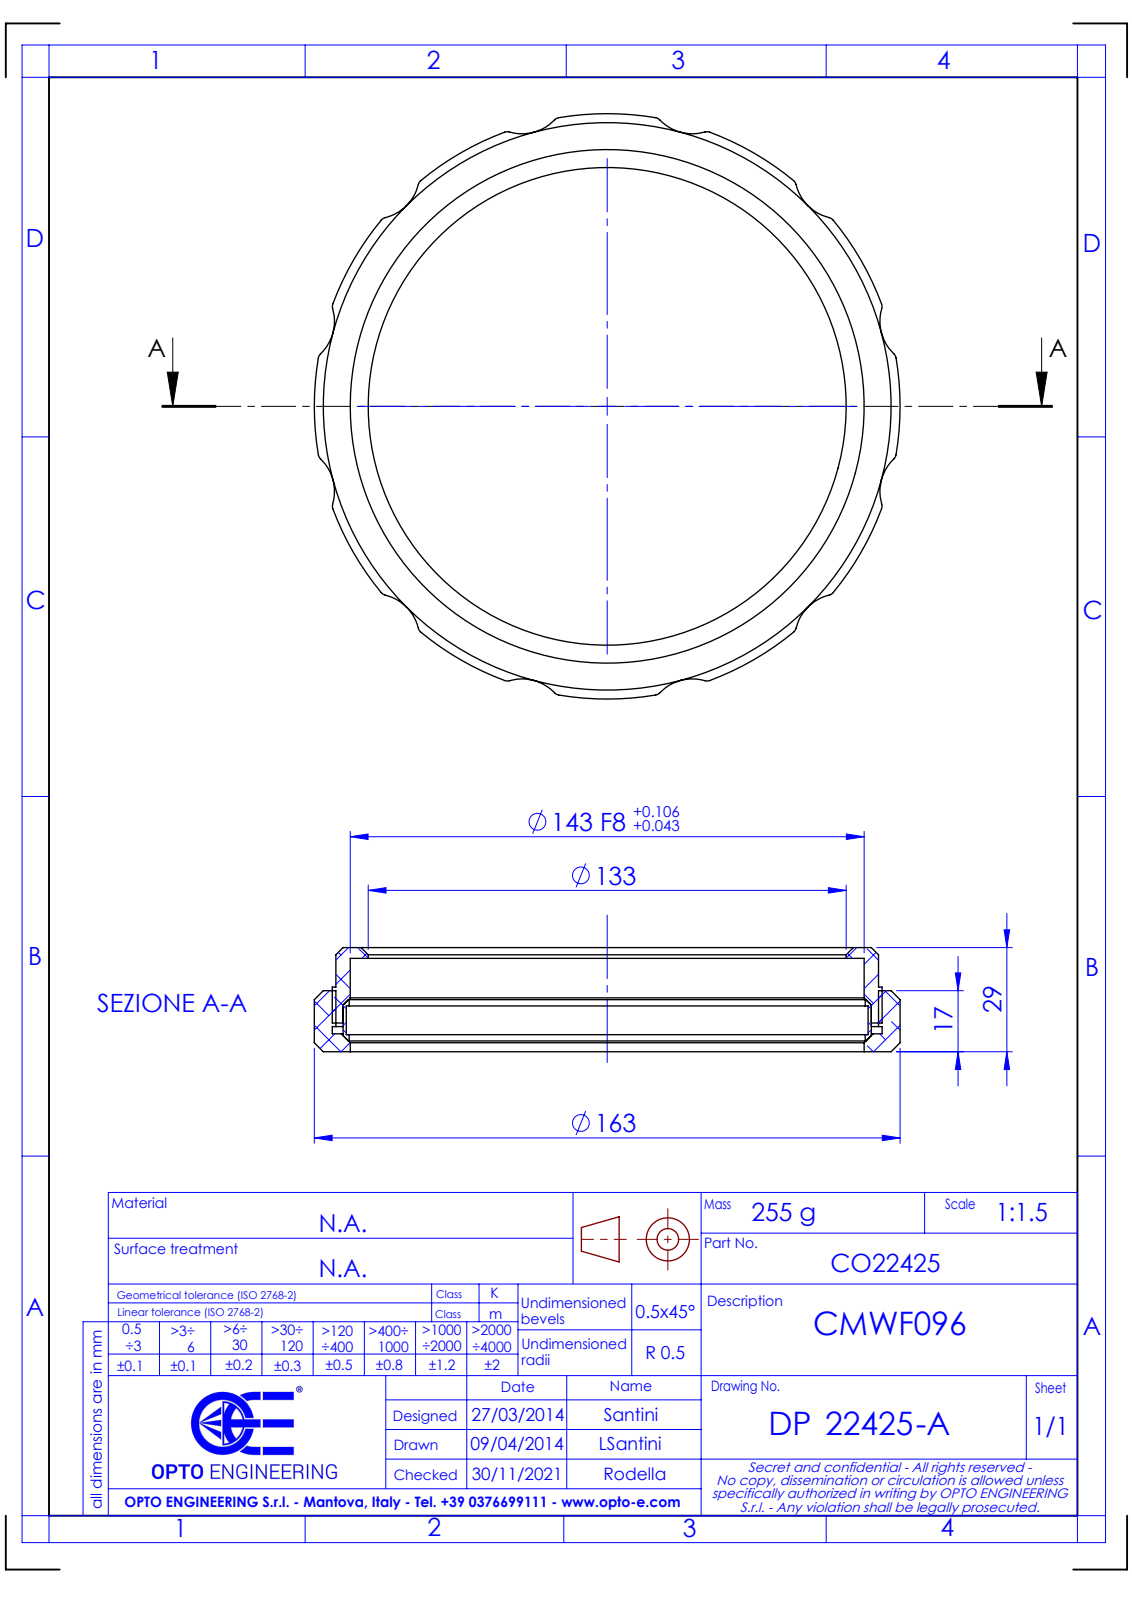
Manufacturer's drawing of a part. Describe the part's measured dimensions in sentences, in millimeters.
The part is named "DP22425 -A_CMWF096". Its 3-D file was written by "SolidWorks 2021 (CONFIG_CONTROL_DESIGN)". It is 0 solids with 144 faces: 14 planar, 92 cylindrical and 38 other. Overall it measures 162.28 by 162.28 by 29 millimeters. Round holes: 1 of diameter 133, 1 of diameter 143, 1 of diameter 143.6, 1 of diameter 145.2, 1 of diameter 147, 1 of diameter 151, 1 of diameter 153. Partial cylindrical surfaces (rounded edges, fillets, slot ends): 24 of radius 2, 12 of radius 12.5, 6 of radius 40, 1 of radius 81.5. The main face-to-face distances are 3, 9, 12, 21, 26, 8, 29, 18, 17, 5.
